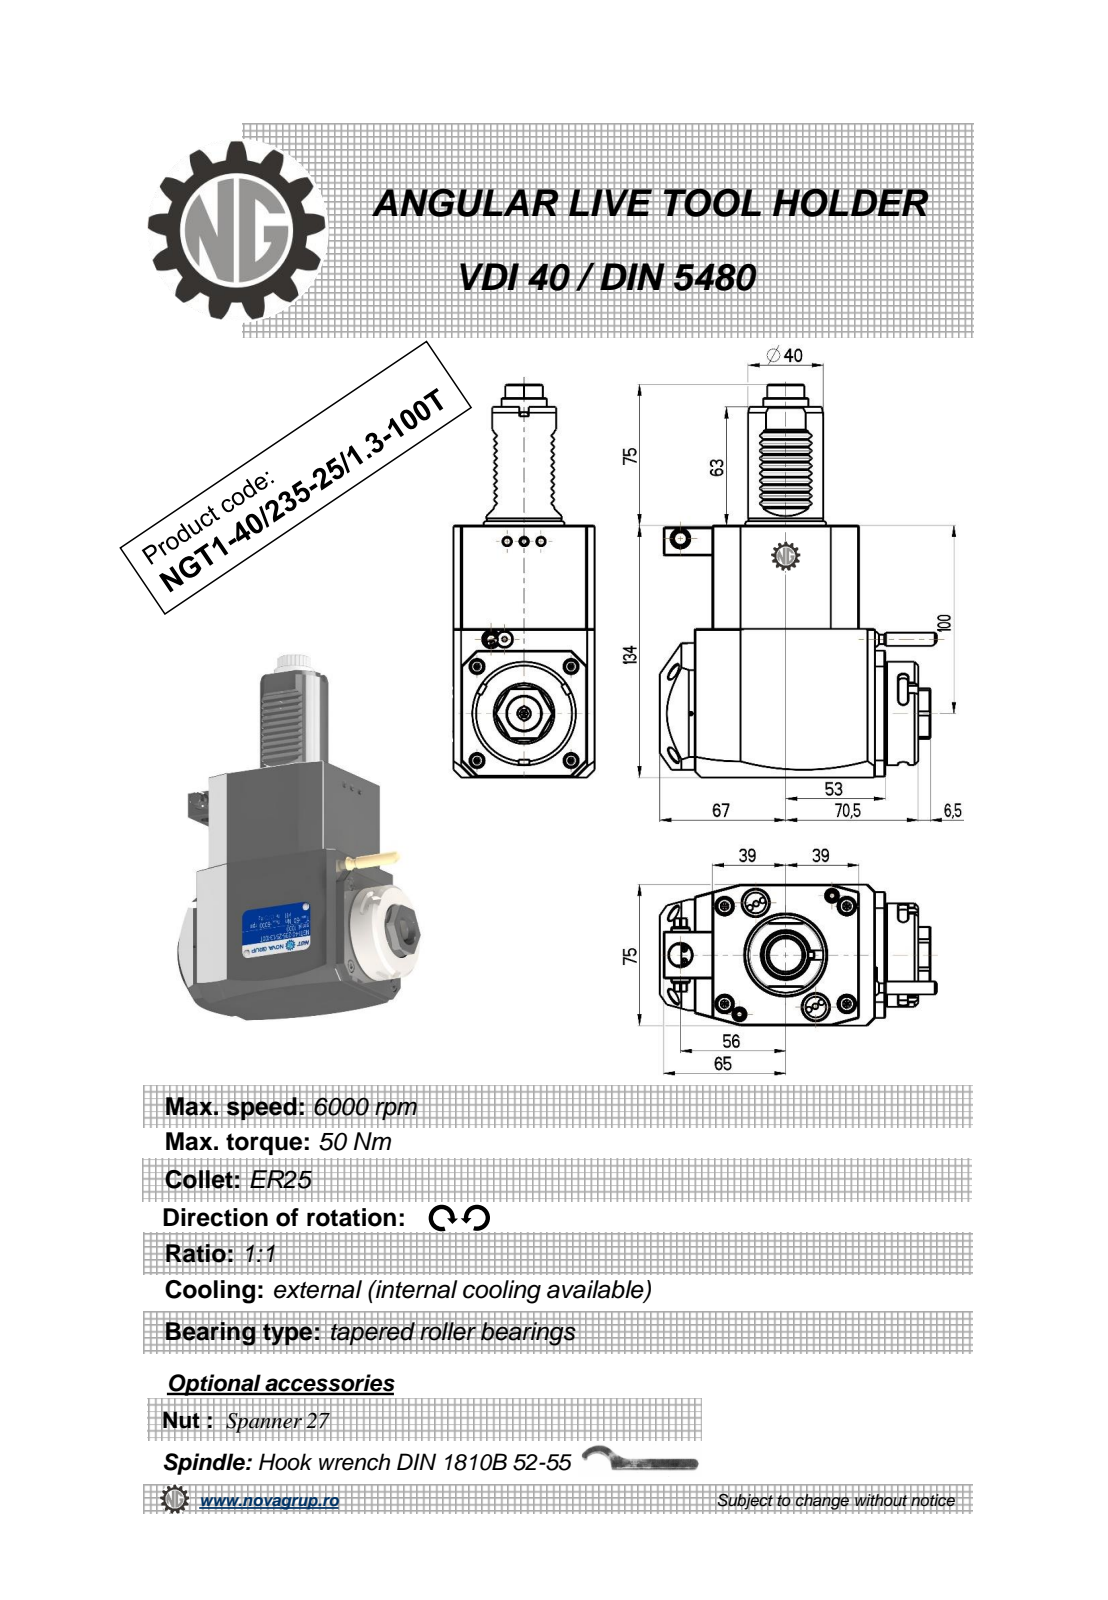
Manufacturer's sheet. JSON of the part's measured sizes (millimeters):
{"part_name": "NGT1_40_235_25_1_3_100T", "step_written_by": "PRO/ENGINEER BY PARAMETRIC TECHNOLOGY CORPORATION, 2010280 (CONFIG_CONTROL_DESIGN)", "units": "millimeters", "bodies": {"solids": 1, "faces": 536, "planar": 226, "cylindrical": 200, "other": 110}, "overall_size": [209, 147.33, 75], "volume_mm3": 1069000, "surface_area_mm2": 77929, "round_holes": [[3.3, 2], [4.5, 2], [7.5, 2], [2.5, 1], [3, 1], [9.5, 1], [12, 1], [18, 1]], "round_bosses_or_shafts": [[8, 2], [55, 1], [48, 1], [40, 1], [24, 1], [10, 1], [7, 1], [5, 1]], "partial_cylinders_radius": [[2.08, 48], [0.3, 20], [2.5, 6], [15, 2], [180, 2], [3.85, 1], [4.25, 1], [9.08, 1]], "face_to_face_distances": [75, 134, 78, 14, 92, 17.5, 31.5, 79, 84.88, 109.5], "hole_center_spacings": [31.11, 18.07, 43.2, 54.87, 62.23, 72.9, 73.09, 91.5]}
